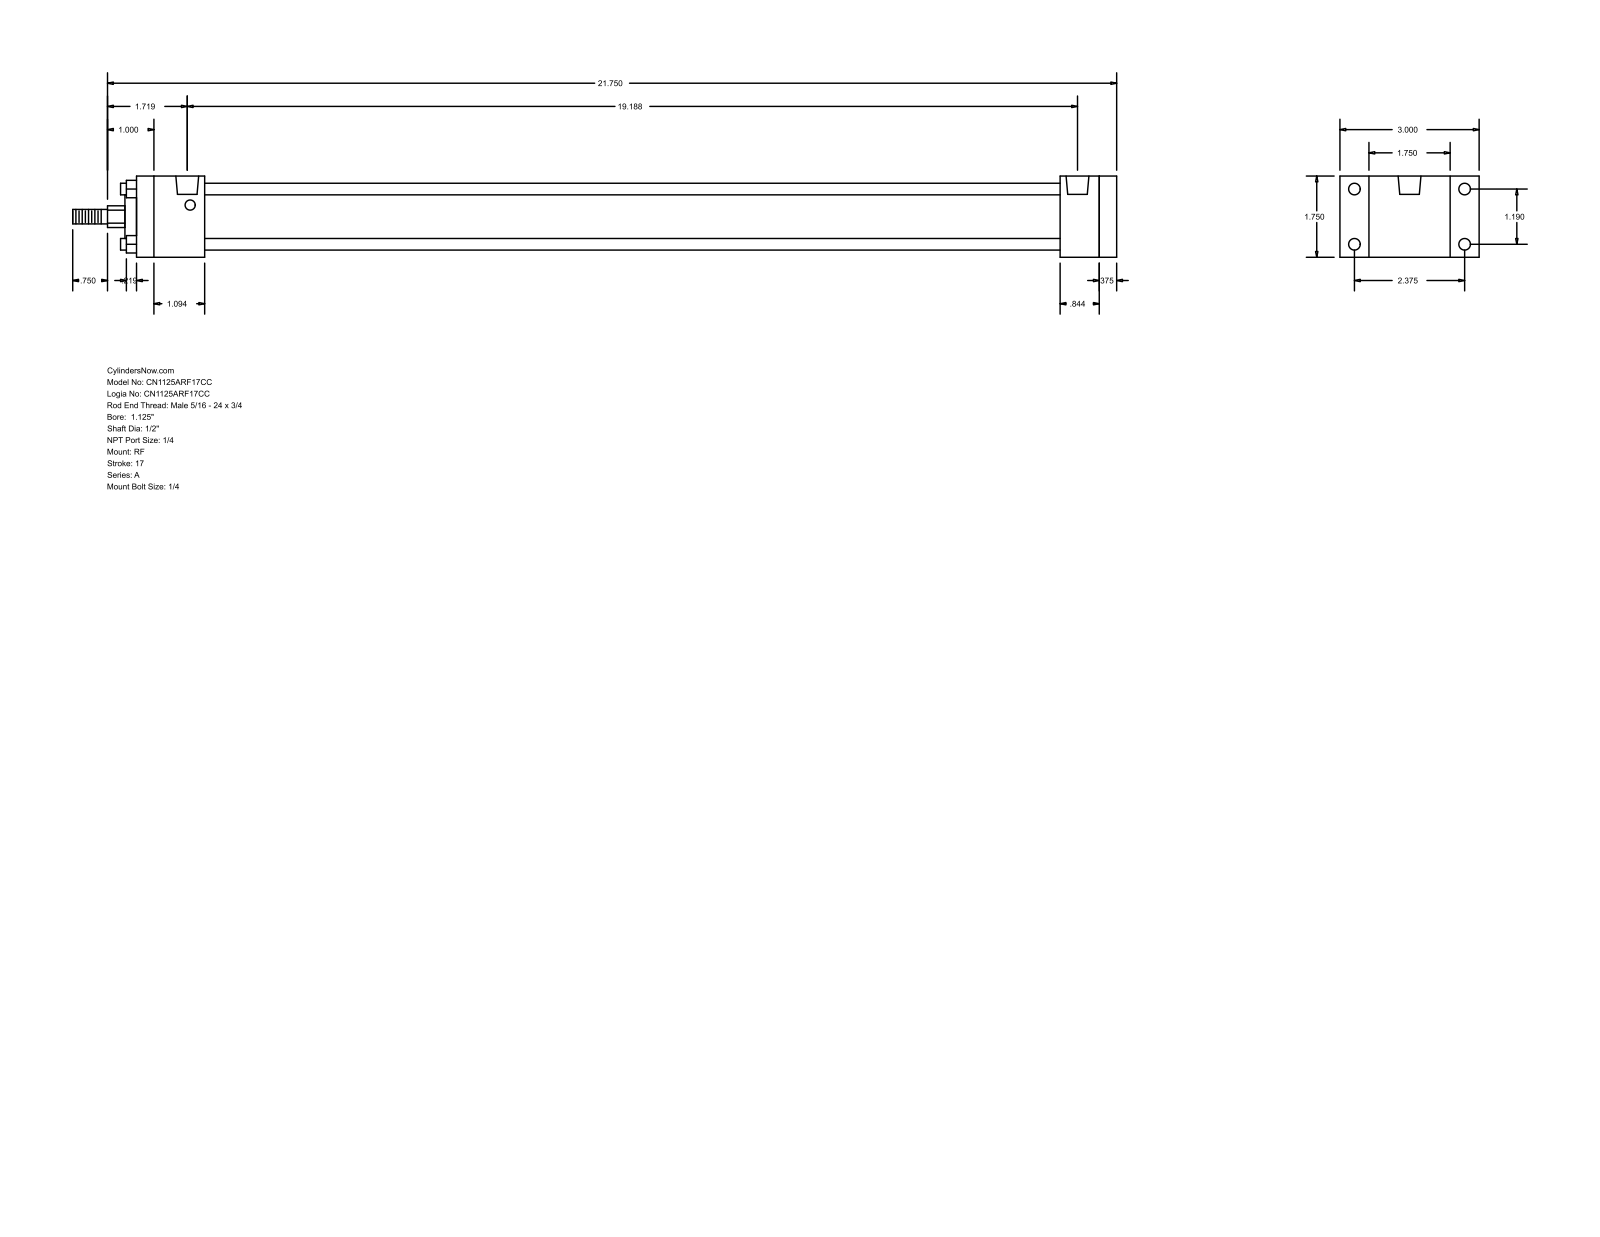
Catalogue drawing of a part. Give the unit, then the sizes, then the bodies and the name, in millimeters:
Units: millimetres
Overall size (bounding box): 571.5 × 76.2 × 44.45
Round holes (diameter × count): ⌀5.56 ×4, ⌀6.35 ×4, ⌀12.49 ×2
Round bosses / shafts (diameter × count): ⌀6.35 ×4, ⌀31.88 ×1, ⌀23.81 ×1, ⌀12.7 ×1, ⌀7.94 ×1
Partial cylindrical surfaces — rounded edges, fillets, slot ends (radius × count): R5.94 ×1
Main face-to-face distances: 44.46, 9.53, 536.57, 527.04, 37.3, 505.61, 468.31, 489.74, 499.27, 21.43
Hole centre spacings: 30.22, 60.32, 67.47, 484.19, 1.58, 1.59, 485.77, 485.78
Bodies: 0 solids, 92 faces (64 planar, 28 cylindrical, 0 other)
Part name (STEP PRODUCT): A_RF__0112_0.5
STEP written by: GSSL Pune (CONFIG_CONTROL_DESIGN)
